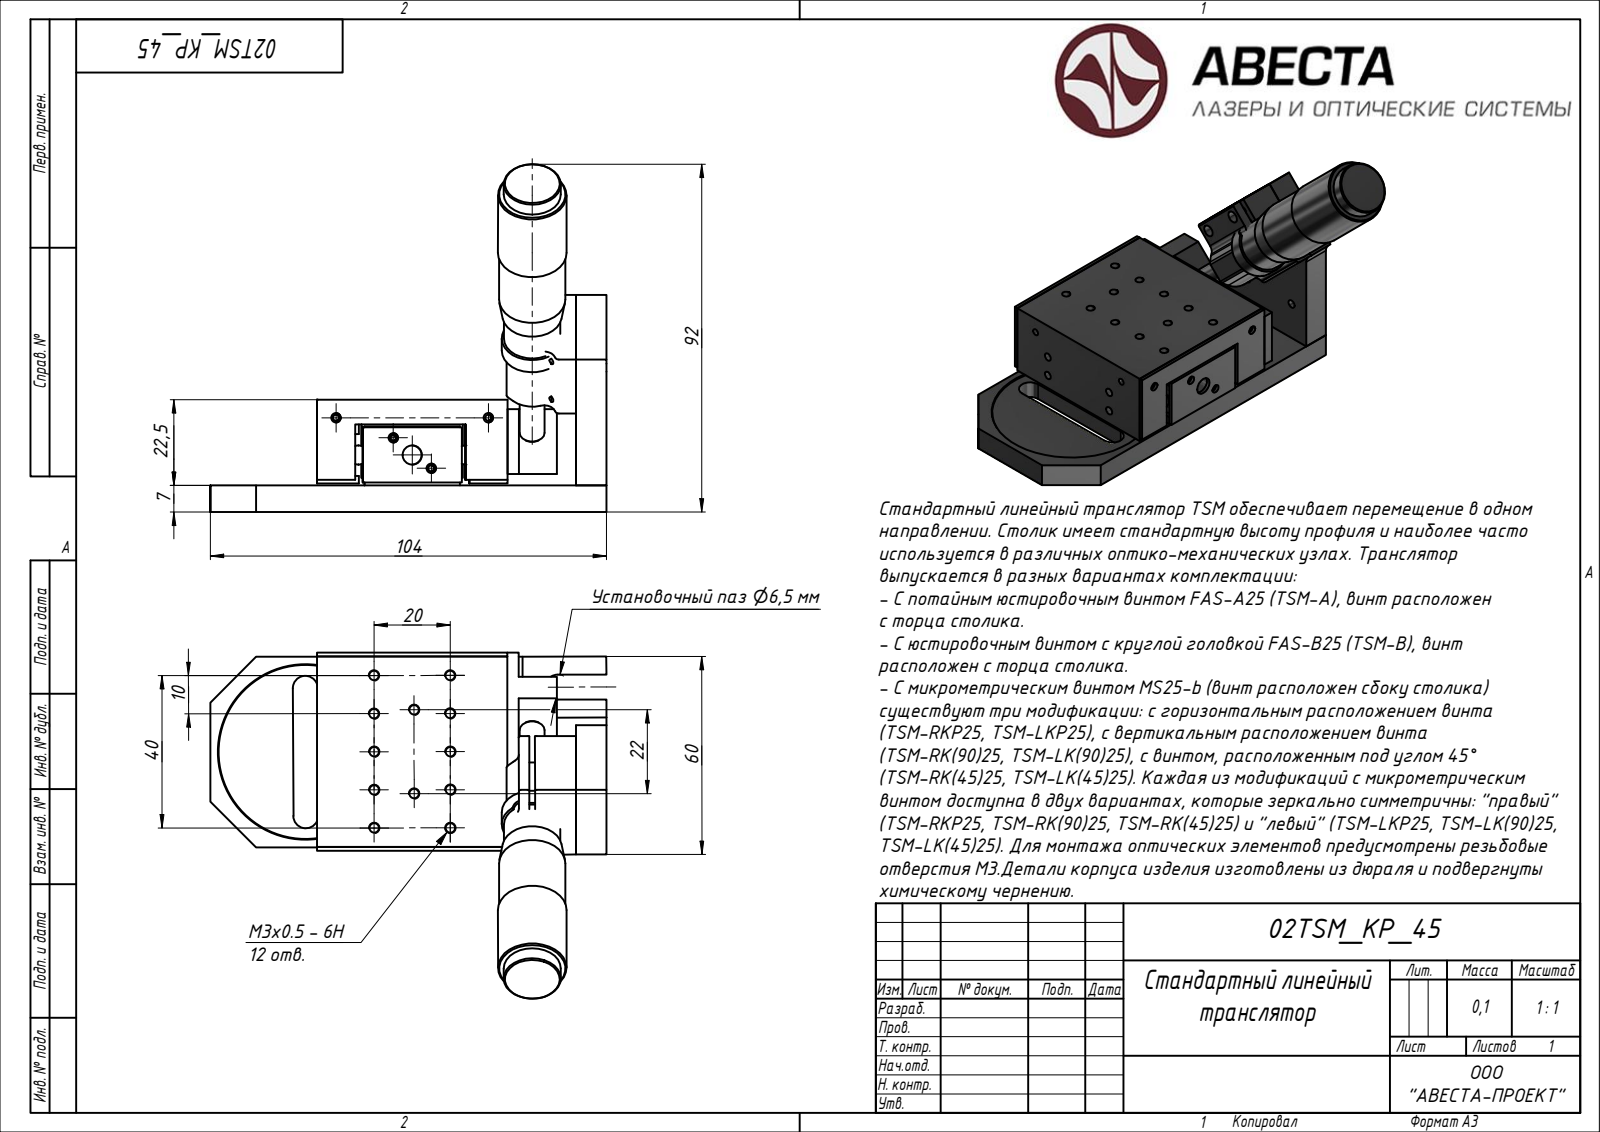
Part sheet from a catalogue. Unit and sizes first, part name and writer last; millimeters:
Units: millimetres
Overall size (bounding box): 107.03 × 92.83 × 91.28
Bodies: 24 solids, 785 faces (0 planar, 0 cylindrical, 785 other)
STEP written by: ST-DEVELOPER v15 (AUTOMOTIVE_DESIGN)
